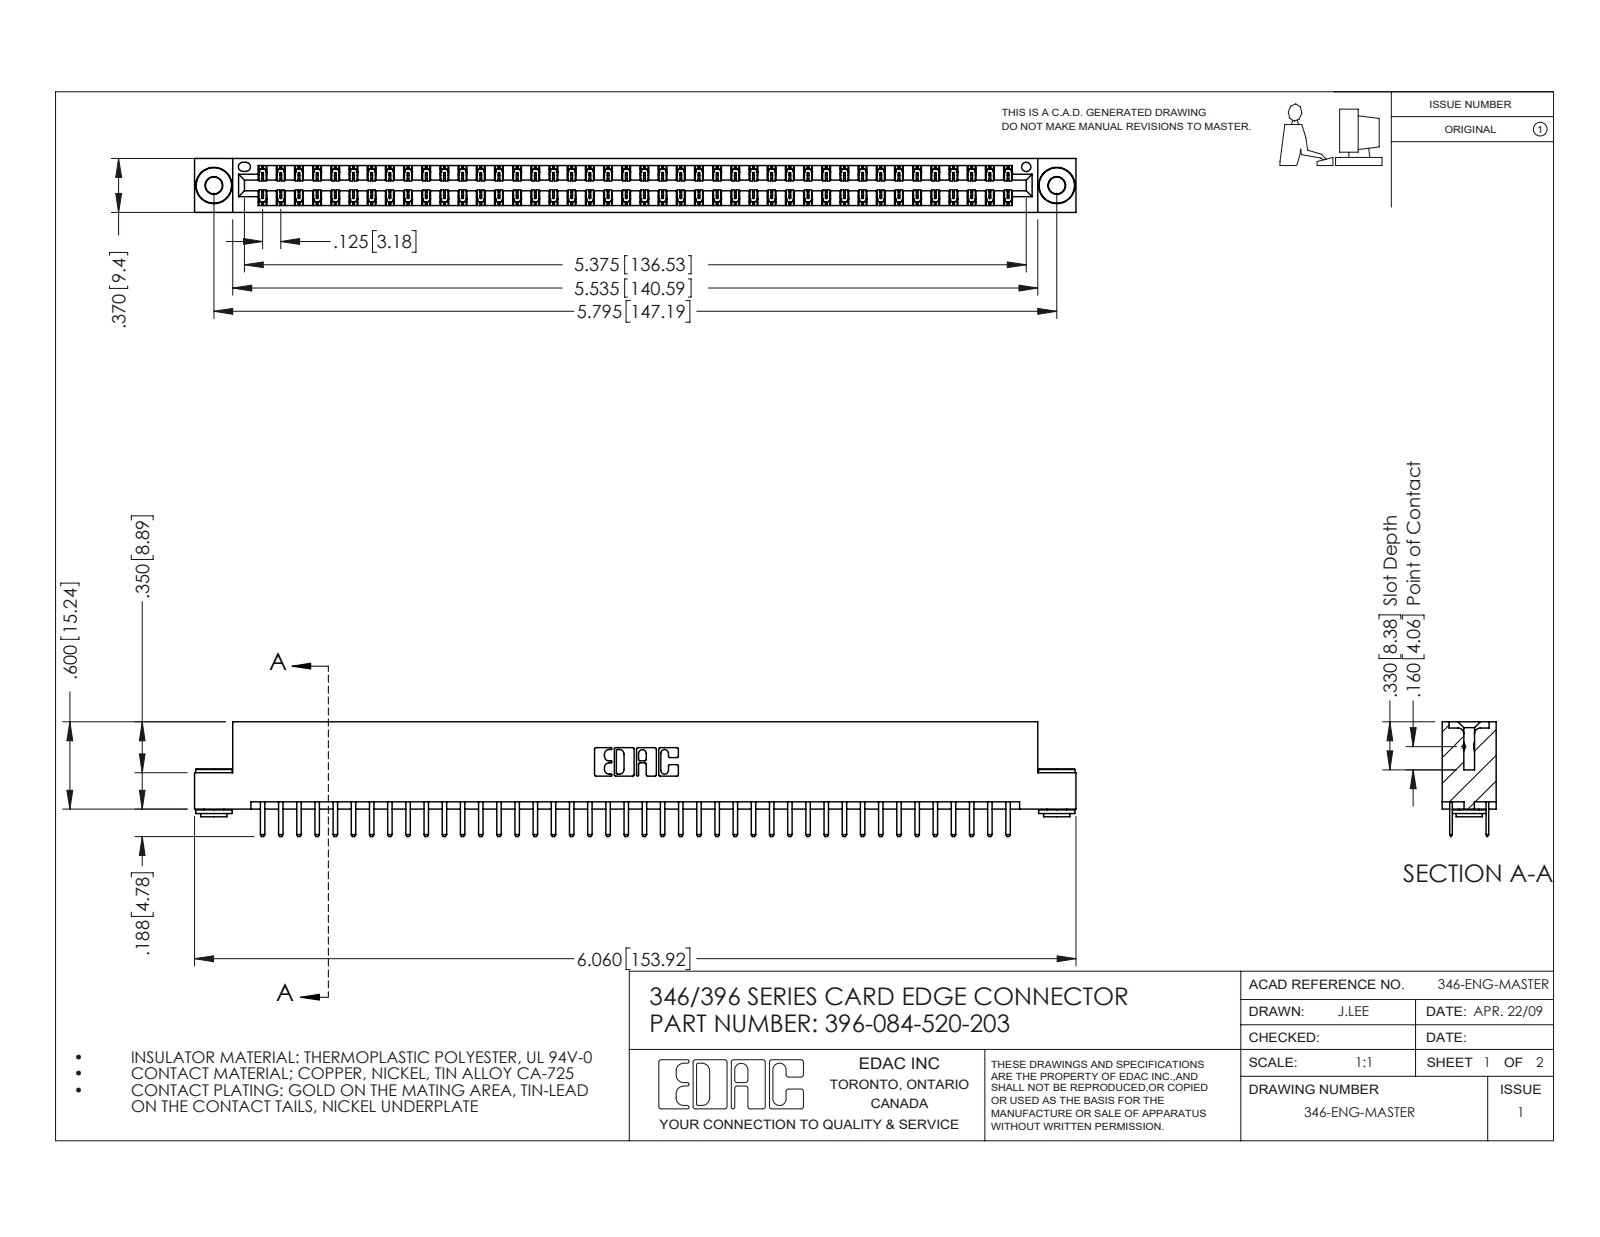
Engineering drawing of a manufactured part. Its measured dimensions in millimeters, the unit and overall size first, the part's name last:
Units: millimetres
Overall size (bounding box): 153.9 × 20 × 9.4
Round holes (diameter × count): ⌀2.9 ×2, ⌀4 ×2, ⌀1.6 ×1
Round bosses / shafts (diameter × count): ⌀6.4 ×2, ⌀4.6 ×2, ⌀3.5 ×2
Partial cylindrical surfaces — rounded edges, fillets, slot ends (radius × count): R0.2 ×126, R0.3 ×88, R0.3 ×22, R0.2 ×6, R0.8 ×6, R0.7 ×3, R0.4 ×2, R0.6 ×2
Main face-to-face distances: 1.2, 8.2, 6.4, 9.4, 0.6, 7, 1.8, 7.6, 3.8, 5.6
Hole centre spacings: 6.2, 141.9, 147.2
Volume: 15 000 mm³ · Surface area: 20 740 mm²
Bodies: 87 solids, 4864 faces (3194 planar, 1662 cylindrical, 8 other)
Part name (STEP PRODUCT): 345-250-002_345-250-002-102; 345-292-001_345-293-120; 396-084-520-203; 346 Part_Flush Mounting Lugs - 0.156 Dia-TH
STEP written by: SolidWorks 2016 (CONFIG_CONTROL_DESIGN)
